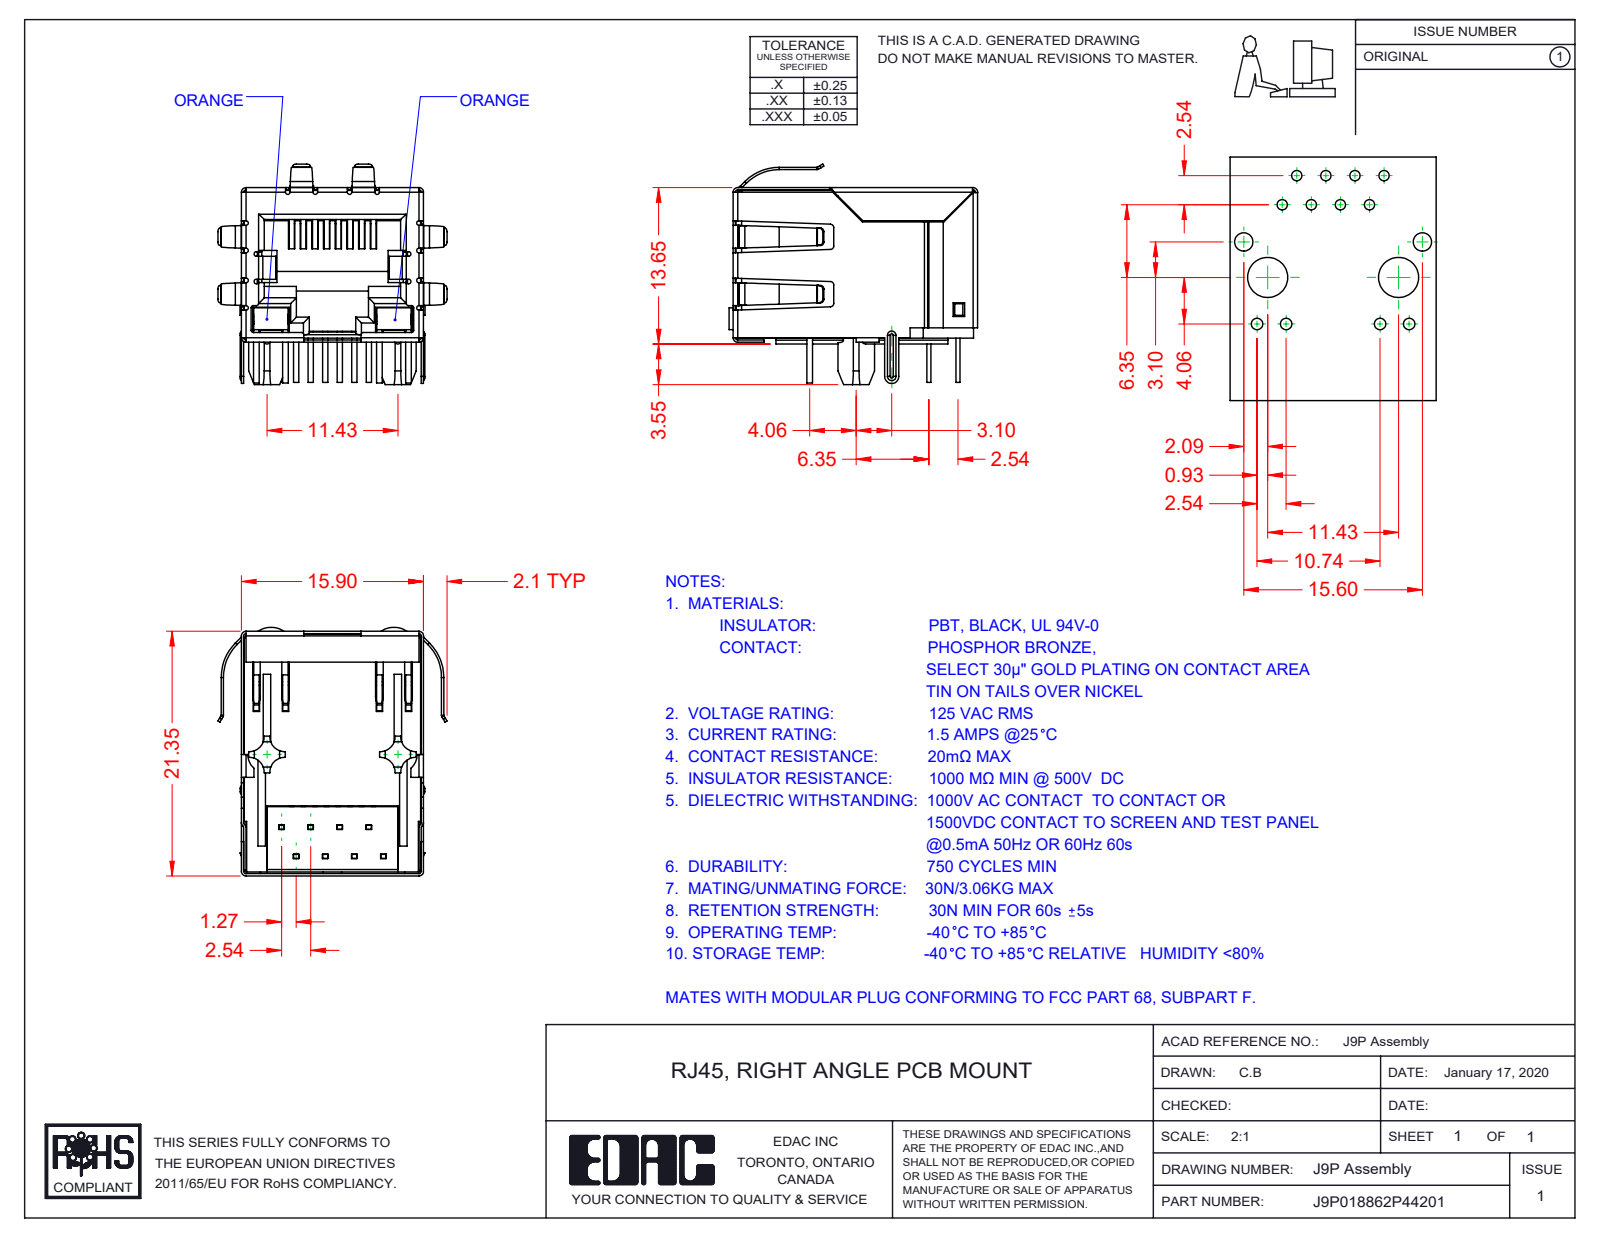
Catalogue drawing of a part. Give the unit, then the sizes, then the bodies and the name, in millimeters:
Units: millimetres
Overall size (bounding box): 21.7 × 20 × 19.25
Partial cylindrical surfaces — rounded edges, fillets, slot ends (radius × count): R0.2 ×39, R0.5 ×22, R0.3 ×20, R0.4 ×16, R1.3 ×8, R0.23 ×5, R0.11 ×4, R0.31 ×4
Main face-to-face distances: 15.45, 15.7, 15.65, 0.35, 0.54, 15.5, 12.36, 0.6, 1.4, 0.59
Volume: 2 687 mm³ · Surface area: 7 515 mm²
Bodies: 13 solids, 1472 faces (1042 planar, 336 cylindrical, 94 other)
Part name (STEP PRODUCT): 9P-LED Shield; 9P-LED Insulator; 9P-LED Assembly; 9P-LED Contacts (+4 more)
STEP written by: SolidWorks 2016 (CONFIG_CONTROL_DESIGN)
